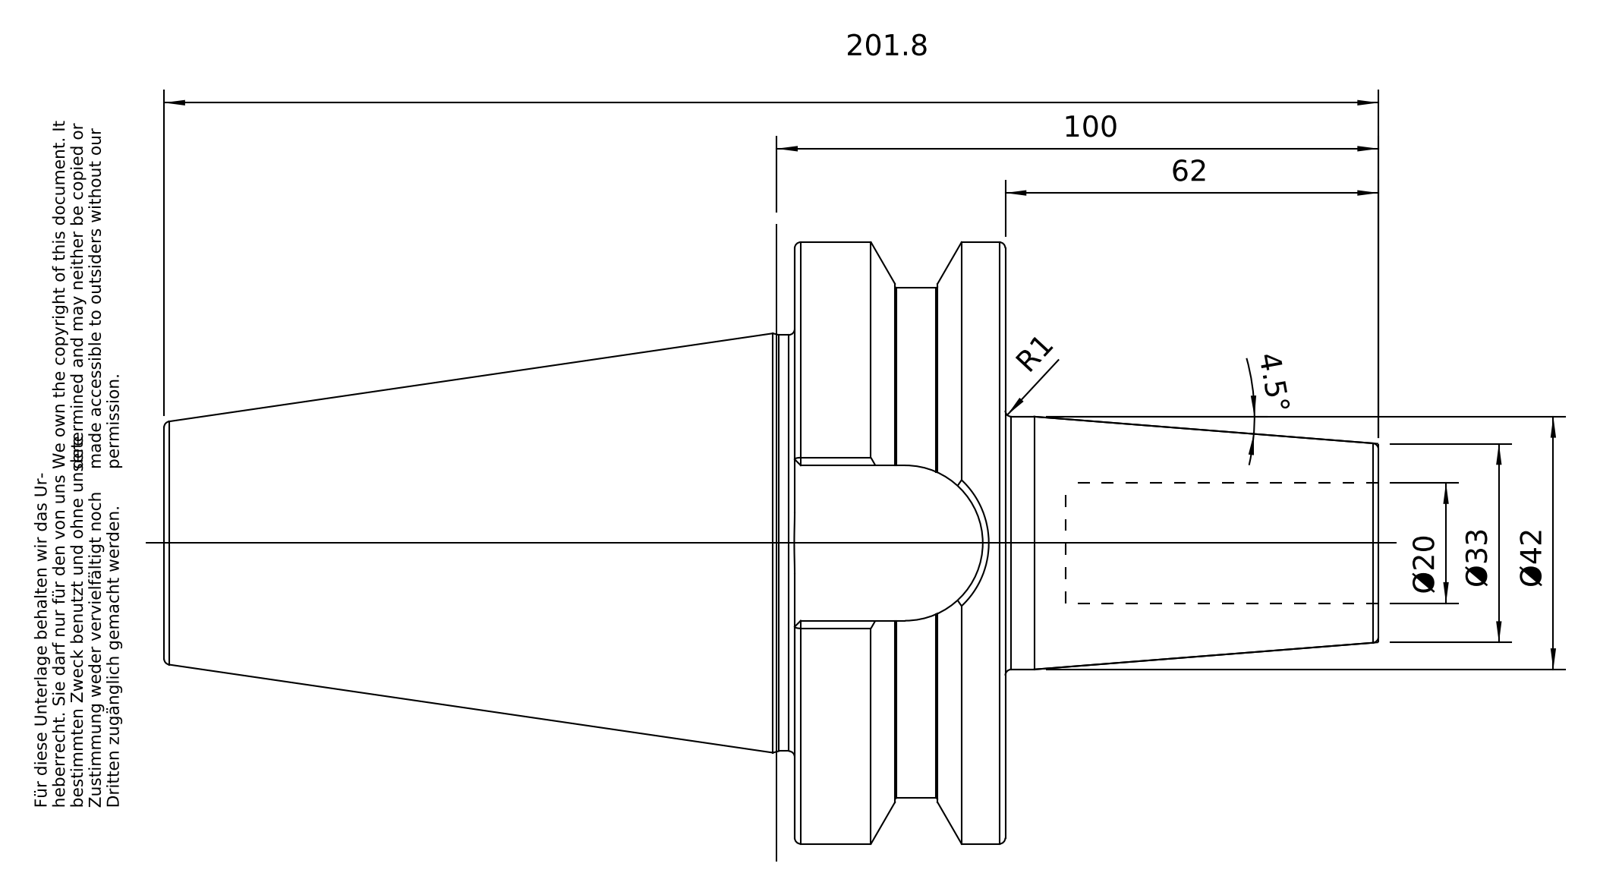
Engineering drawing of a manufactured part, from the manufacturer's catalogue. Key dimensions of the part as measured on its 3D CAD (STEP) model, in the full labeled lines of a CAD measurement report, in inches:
Part name (STEP PRODUCT): 50-640-20
STEP written by: PRO/ENGINEER BY PARAMETRIC TECHNOLOGY CORPORATION, 2010430 (CONFIG_CONTROL_DESIGN)
Units: inches
Bodies: 1 solid, 96 faces (26 planar, 22 cylindrical, 48 other)
Overall size (bounding box): 7.945 × 3.936 × 3.936
Volume: 31.85 in³ · Surface area: 95.92 in²
Round holes (diameter × count): ⌀0.787 ×1, ⌀0.817 ×1, ⌀0.985 ×1, ⌀1.012 ×1
Round bosses / shafts (diameter × count): ⌀3.936 ×1, ⌀3.337 ×1, ⌀2.722 ×1, ⌀1.654 ×1, ⌀0.945 ×1
Partial cylindrical surfaces — rounded edges, fillets, slot ends (radius × count): R0.508 ×1
Main face-to-face distances: 1.378, 2.772, 4.126, 5.504, 7.945, 3.819, 2.441, 1.016, 5.898, 1.772
